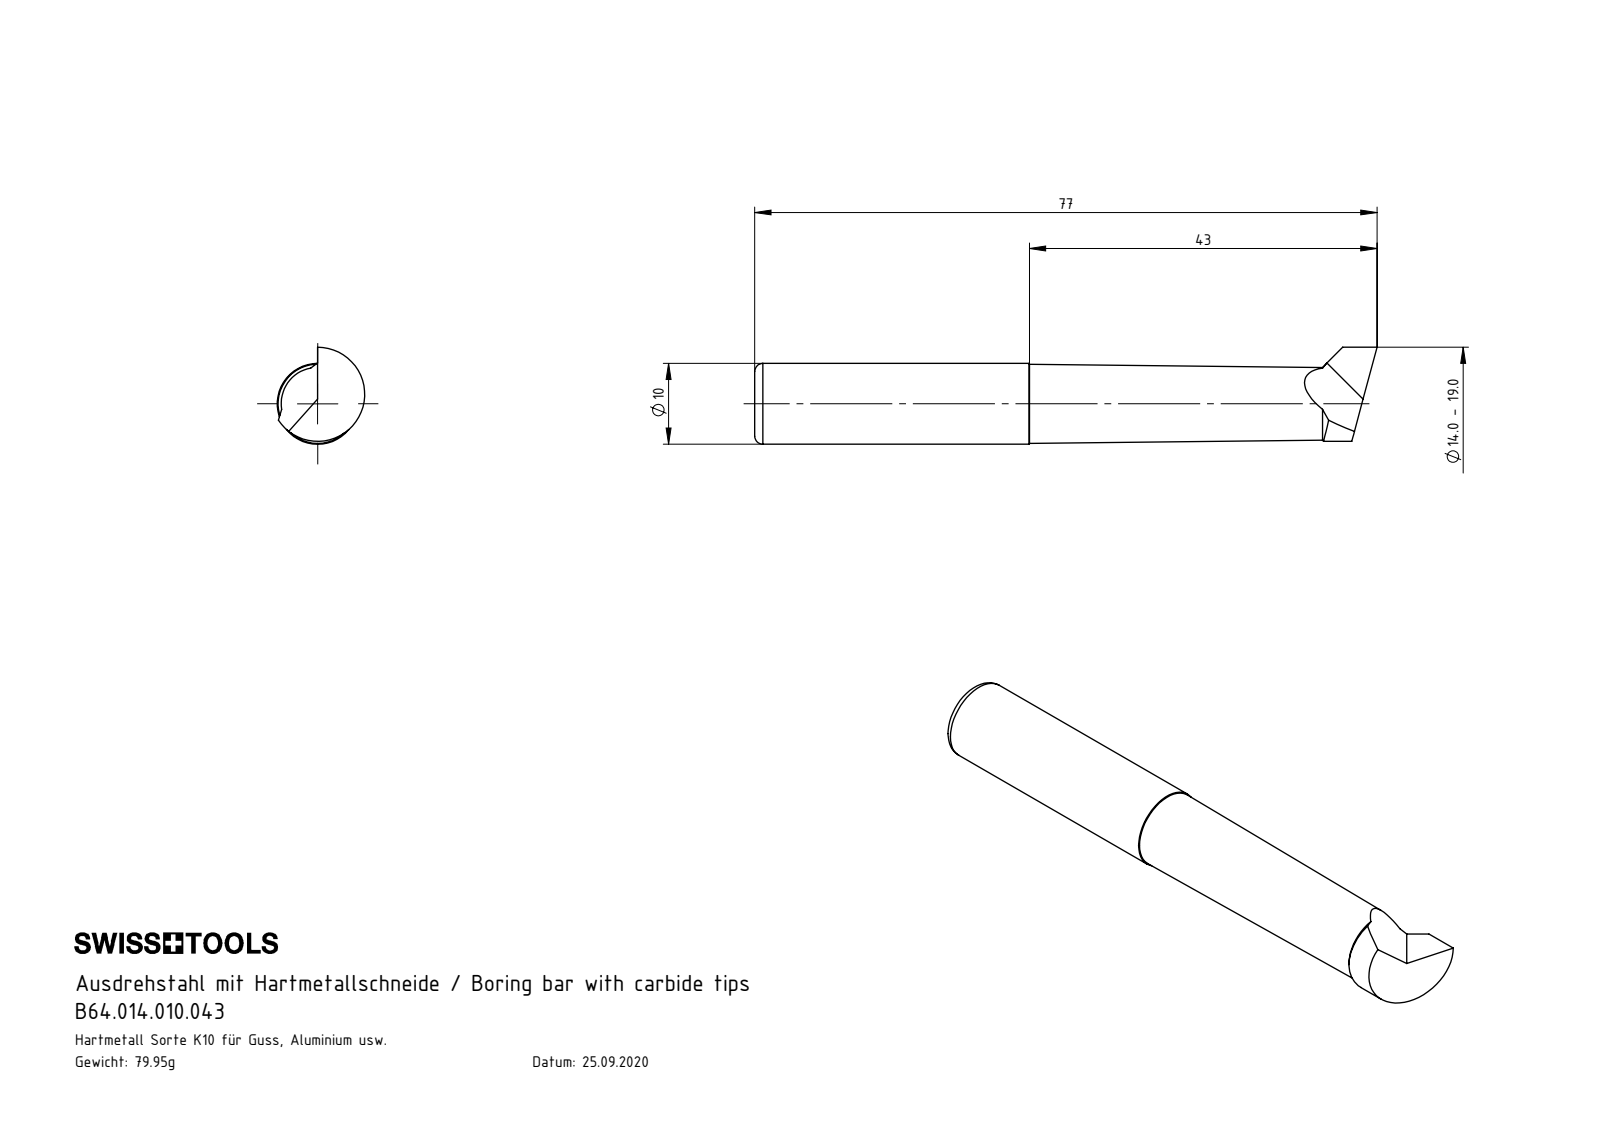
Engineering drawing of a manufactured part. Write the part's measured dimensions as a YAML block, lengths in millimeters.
part_name: "B64.014.010.043"
step_written_by: "SolidWorks 2022 (CONFIG_CONTROL_DESIGN)"
units: millimeters
bodies: {solids: 1, faces: 16, planar: 4, cylindrical: 3, other: 9}
overall_size: [77, 12, 10.82]
volume: 5514
surface_area: 2452
round_bosses_or_shafts:
  - {diameter: 10, count: 1}
partial_cylinders:
  - {radius: 5.82, count: 1}
